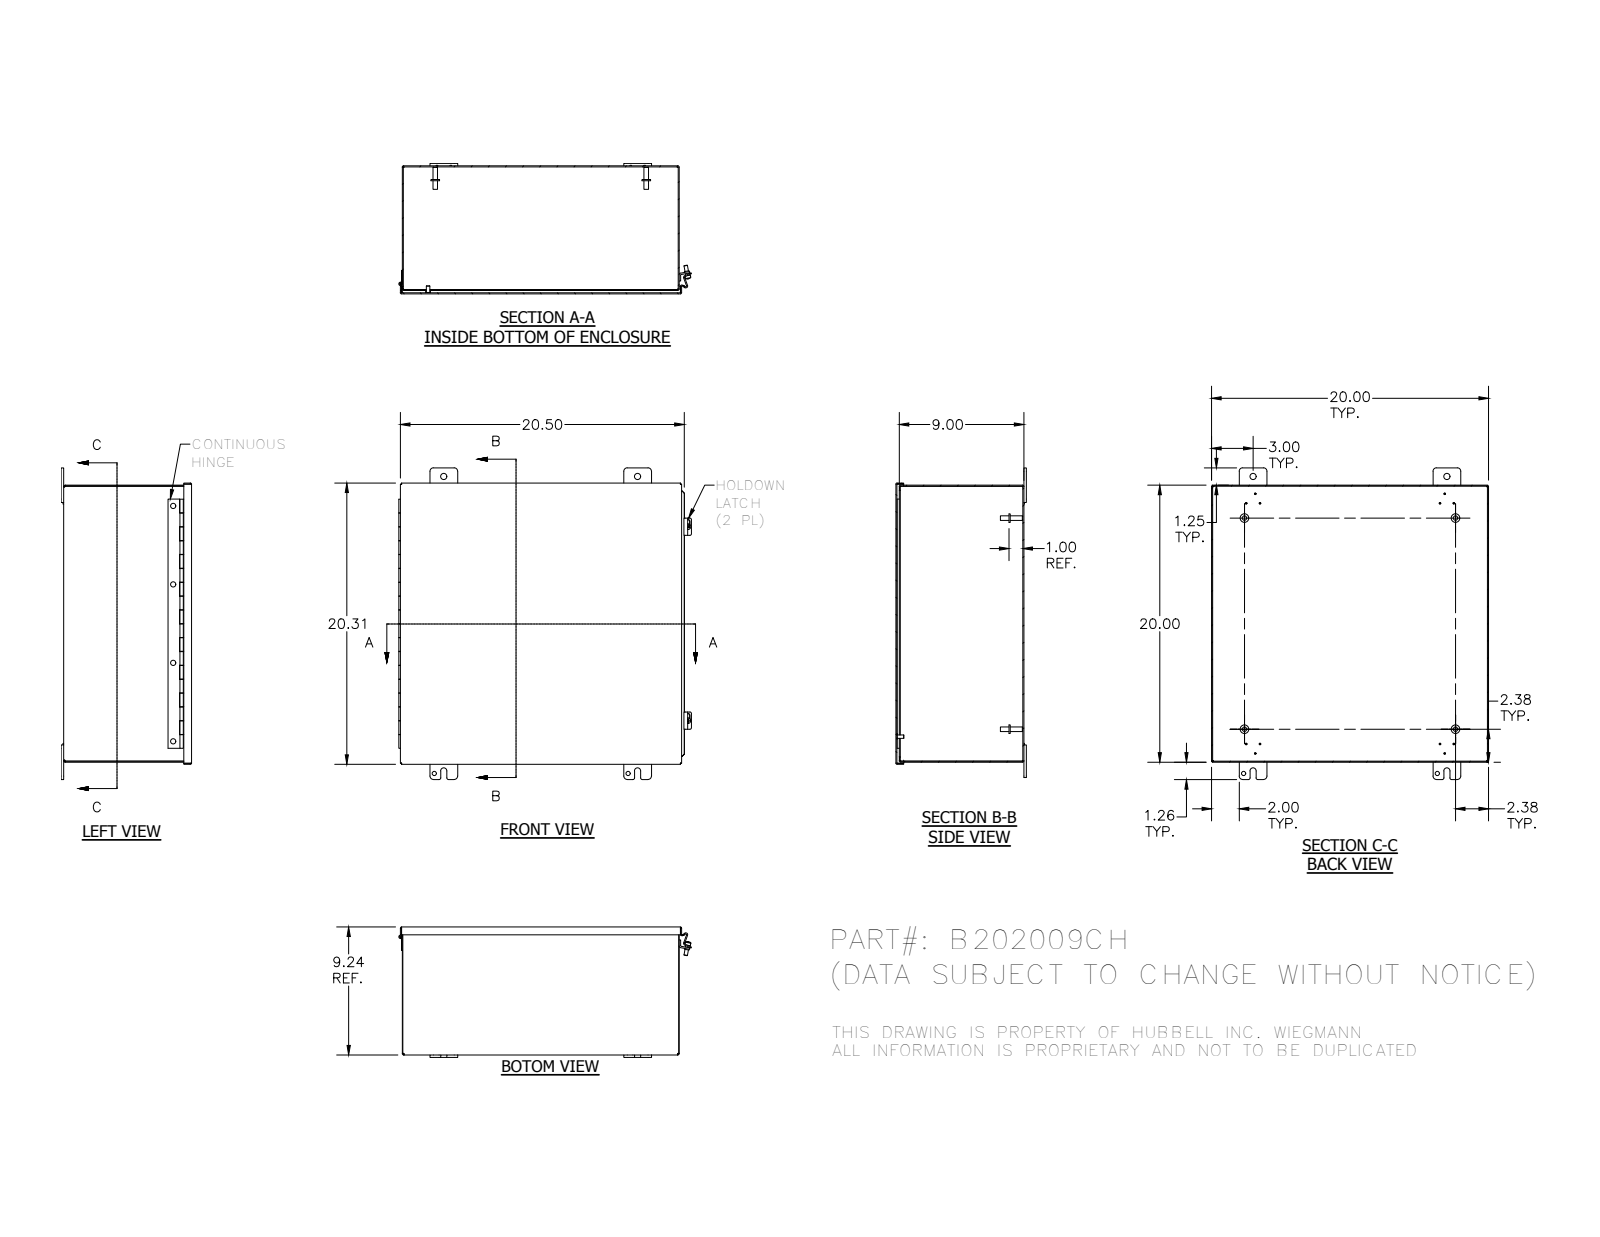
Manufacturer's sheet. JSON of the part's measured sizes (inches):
{"part_name": "B202009CH; B202009CHBKP; B2020CHLID; H6010100 (+8 more)", "step_written_by": "Autodesk Inventor 2012 (AUTOMOTIVE_DESIGN)", "units": "inches", "bodies": {"solids": 20, "faces": 617, "planar": 371, "cylindrical": 177, "other": 69}, "overall_size": [22.505, 21.136, 9.423], "volume_in3": 124, "surface_area_in2": 3338, "round_holes": [[0.11, 4], [0.313, 4], [0.375, 4], [0.438, 4], [0.196, 2], [0.125, 1], [0.125, 1]], "round_bosses_or_shafts": [[0.625, 4], [0.33, 4], [0.25, 4], [0.41, 2], [0.344, 2], [0.337, 1], [0.12, 1]], "partial_cylinders_radius": [[0.125, 16], [0.25, 16], [0.031, 8], [0.063, 8], [0.07, 8], [0.105, 8], [0.016, 5], [0.09, 5]], "face_to_face_distances": [0.074, 9.169, 19.926, 9.243, 9.095, 20, 19.852, 20.063, 0.137, 8.926], "hole_center_spacings": [14, 1.593, 20.005, 24.417, 0.75, 5.667, 13.39, 14]}
